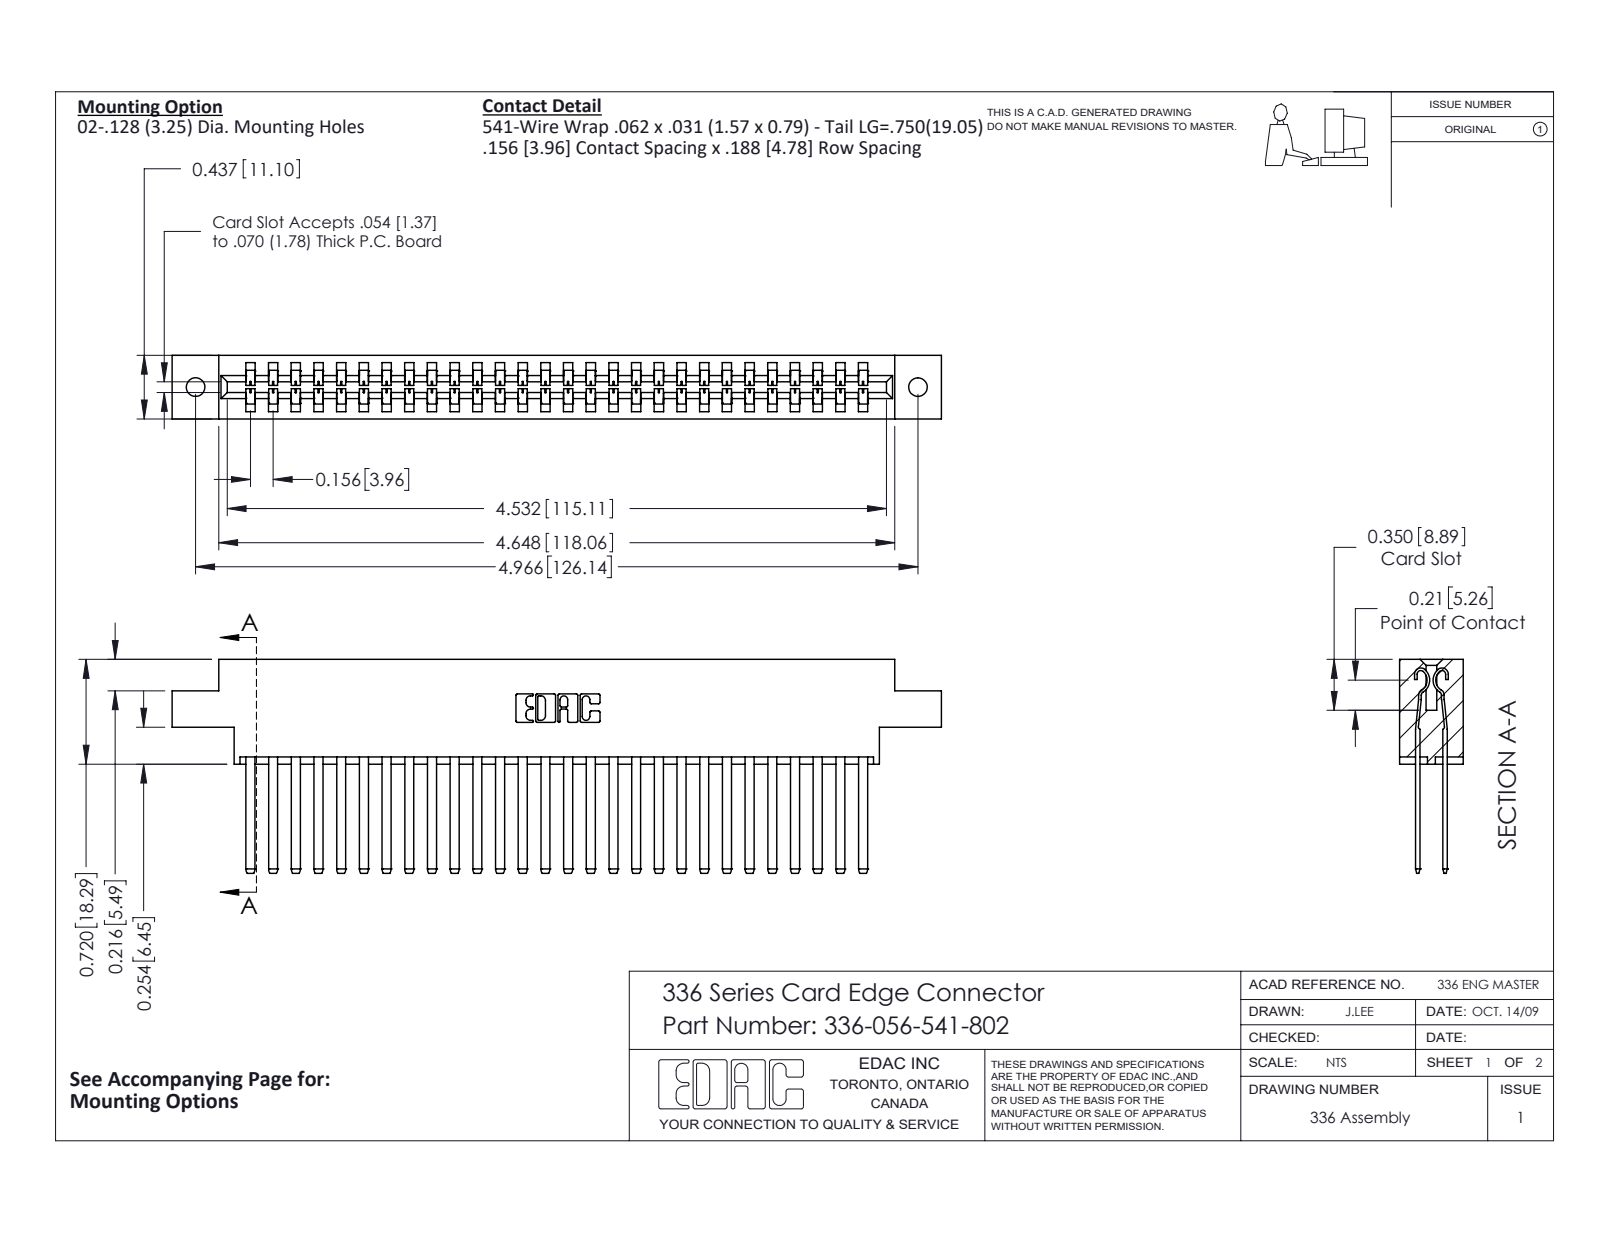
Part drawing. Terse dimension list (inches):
name: 336-056-541-802; 336-290-001_336-290-541; 336 Part_Offset - .128 Dia
written by: SolidWorks 2020 (CONFIG_CONTROL_DESIGN)
unit: in
bodies: 57 solids, 2470 faces (1530 planar, 940 cylindrical, 0 other)
size: 5.289 × 1.47 × 0.437
volume: 1.228 in³; area: 39.4 in²
holes: 2× ⌀0.128
rounds: 112× R0.004, 56× R0.056, 22× R0.01, 6× R0.007, 6× R0.031, 4× R0.022, 4× R0.04, 3× R0.026
face distances: 0.188, 0.328, 0.14, 0.297, 0.109, 0.031, 0.437, 0.033, 0.181, 0.256
hole spacings: 4.966
